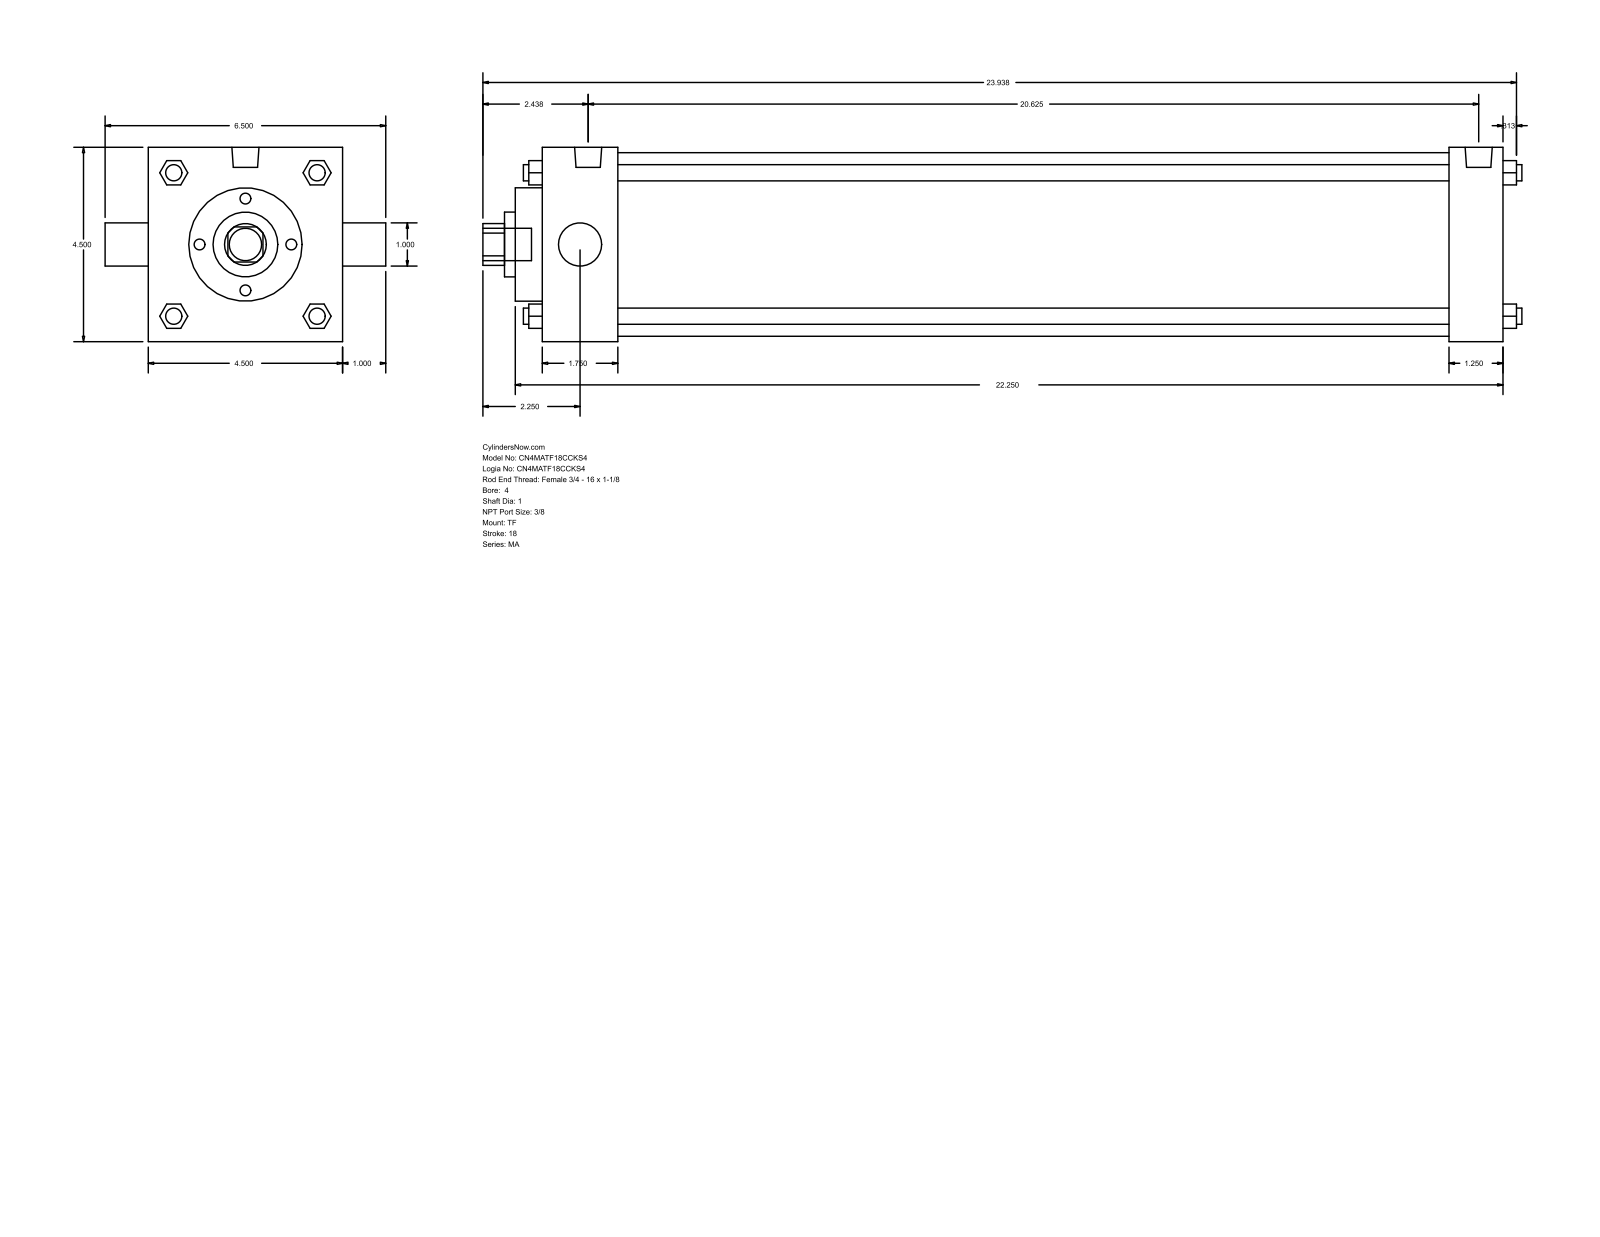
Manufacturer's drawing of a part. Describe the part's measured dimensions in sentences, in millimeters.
The part is named "MA_TF__0400_1". Its 3-D file was written by "GSSL Pune (CONFIG_CONTROL_DESIGN)". It is 0 solids with 122 faces: 93 planar, 29 cylindrical and 0 other. Overall it measures 611.19 by 165.1 by 114.3 millimeters. Round holes: 2 of diameter 25.4, 1 of diameter 38.1, 1 of diameter 66.67, 1 of diameter 107.95. Round bosses or shafts: 4 of diameter 9.53, 3 of diameter 11.11, 2 of diameter 15.93, 1 of diameter 19.05. Partial cylindrical surfaces (rounded edges, fillets, slot ends): 1 of radius 12.29. The main face-to-face distances are 114.3, 565.16, 533.41, 31.75, 44.46, 488.95, 520.7, 15.87, 60.33, 549.28.
